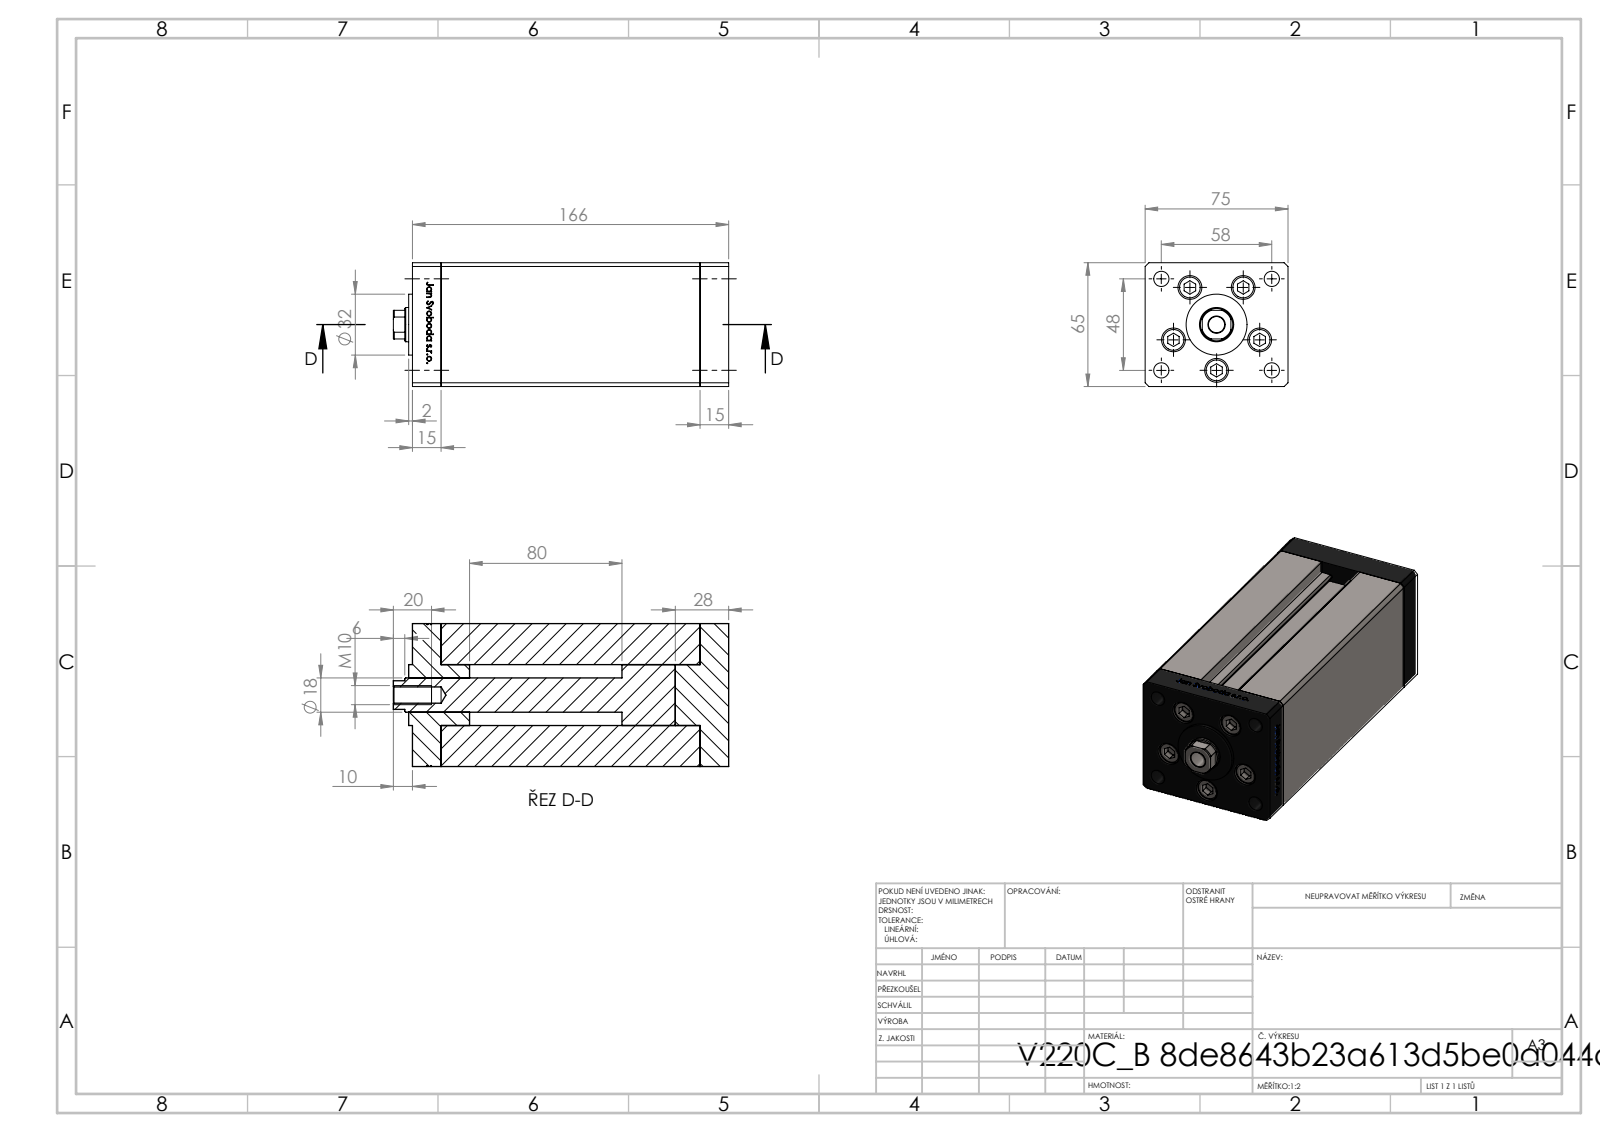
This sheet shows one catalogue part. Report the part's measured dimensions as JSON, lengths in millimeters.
{"part_name": "V220C_VC_B; ALLEN BOLT; V220C BACK_B; V220C_B MIDDLE (+1 more)", "step_written_by": "SolidWorks 2019 (CONFIG_CONTROL_DESIGN)", "units": "millimeters", "bodies": {"solids": 14, "faces": 1183, "planar": 462, "cylindrical": 147, "other": 574}, "overall_size": [176, 75, 65], "volume_mm3": 722498, "surface_area_mm2": 127363, "round_holes": [[9, 5], [12.5, 5], [8, 4], [2, 2], [13.16, 2], [8.5, 1], [18, 1]], "round_bosses_or_shafts": [[8, 5], [32, 1]], "partial_cylinders_radius": [[0.93, 2], [8.5, 1]], "face_to_face_distances": [75, 65, 15, 136, 151, 166, 28, 13, 54.5, 10.5], "hole_center_spacings": [24, 37.64, 15.67, 17.22, 27.71, 28.83, 29, 32.63]}
